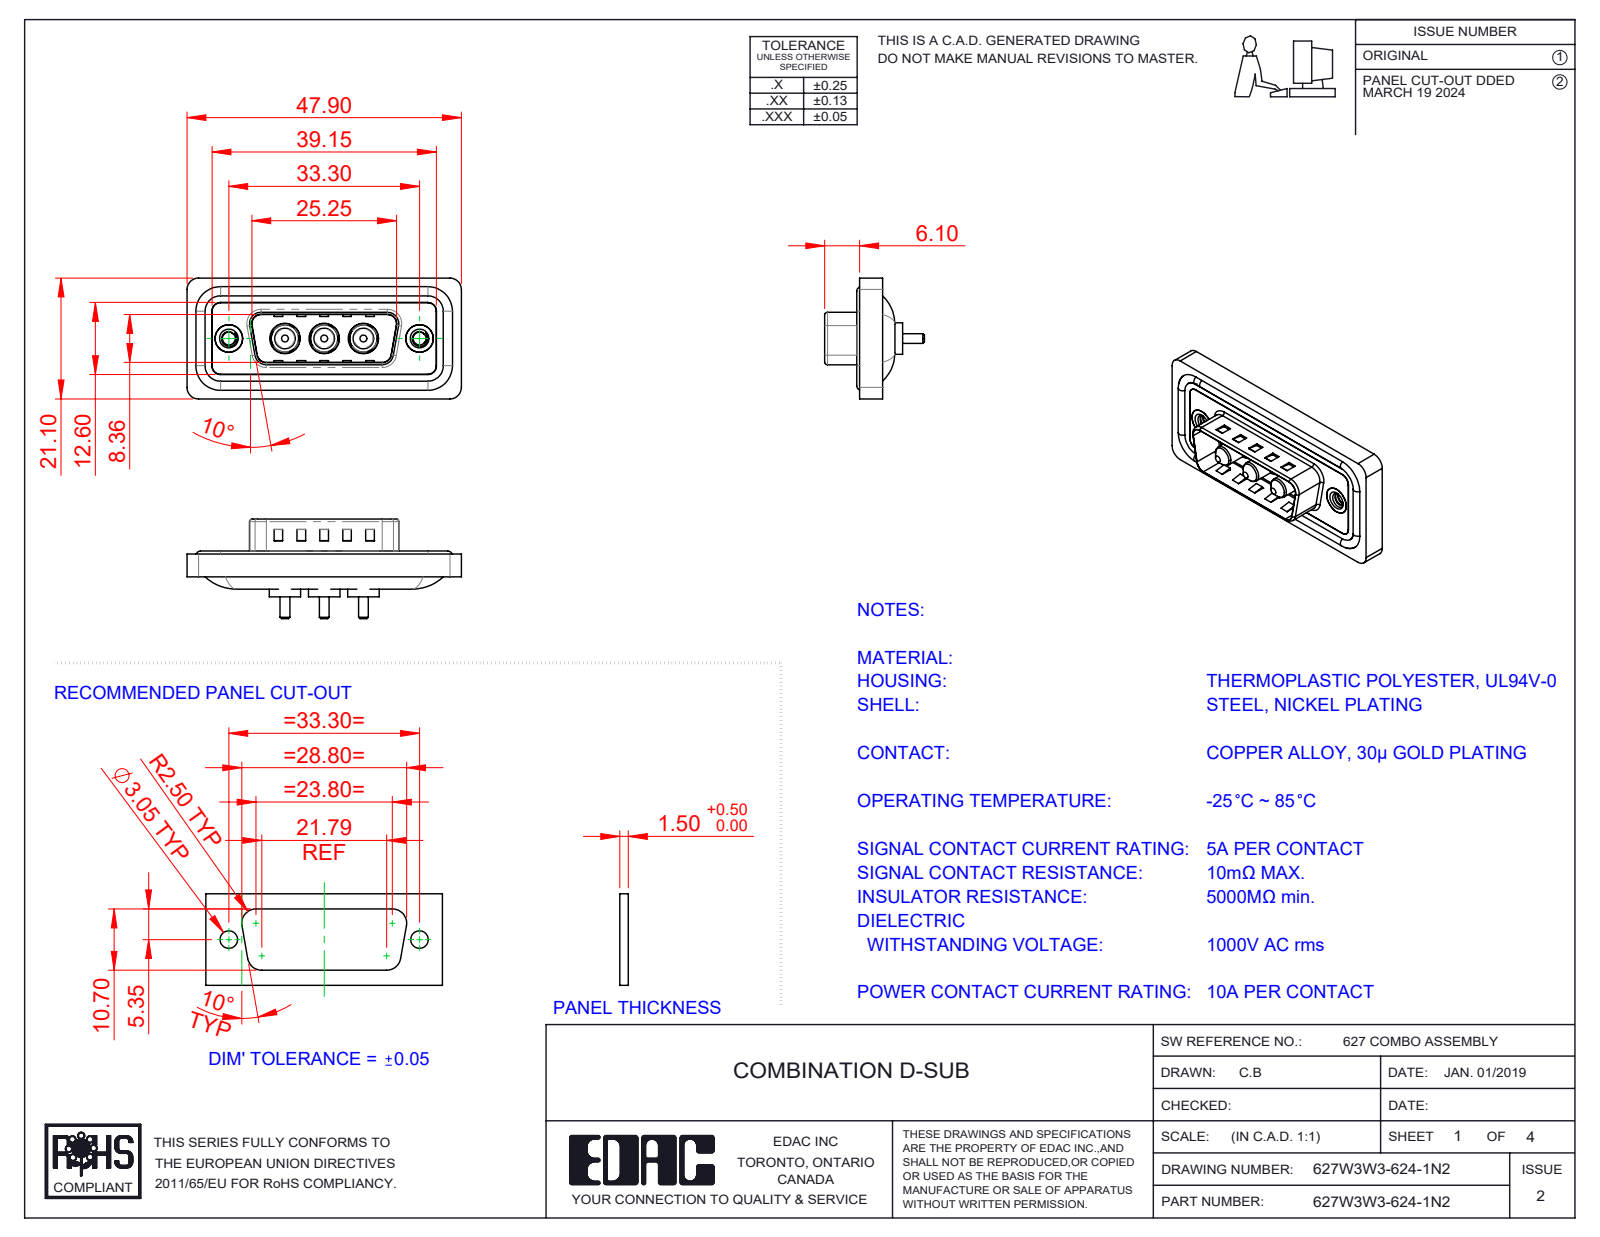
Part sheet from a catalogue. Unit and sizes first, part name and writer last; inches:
Units: inches
Overall size (bounding box): 1.886 × 0.831 × 0.685
Round holes (diameter × count): ⌀0.191 ×3, ⌀0.209 ×3, ⌀0.089 ×2, ⌀0.157 ×2, ⌀0.189 ×2, ⌀0.197 ×2
Round bosses / shafts (diameter × count): ⌀0.063 ×4, ⌀0.217 ×3, ⌀0.205 ×3, ⌀0.187 ×3, ⌀0.148 ×3, ⌀0.142 ×3, ⌀0.067 ×3, ⌀0.193 ×2
Partial cylindrical surfaces — rounded edges, fillets, slot ends (radius × count): R0.059 ×26, R0.079 ×20, R0.02 ×8, R0.063 ×8, R0.01 ×4, R0.024 ×4, R0.026 ×4, R0.035 ×4
Main face-to-face distances: 0.016, 0.059, 0.043, 0.02, 0.063, 0.122, 0.114, 0.157, 0.032, 0.377
Hole centre spacings: 0.27, 0.386, 0.656, 0.925, 0.539, 1.311
Volume: 0.338 in³ · Surface area: 13.51 in²
Bodies: 13 solids, 564 faces (207 planar, 241 cylindrical, 116 other)
Part name (STEP PRODUCT): 627Combo Waterproof Housing_15 Contacts; Power Pin_10A S; 627Combo Shell Rear_15 Contacts; 627W3W3-624-1N2 (+3 more)
STEP written by: SolidWorks 2023 (CONFIG_CONTROL_DESIGN)
